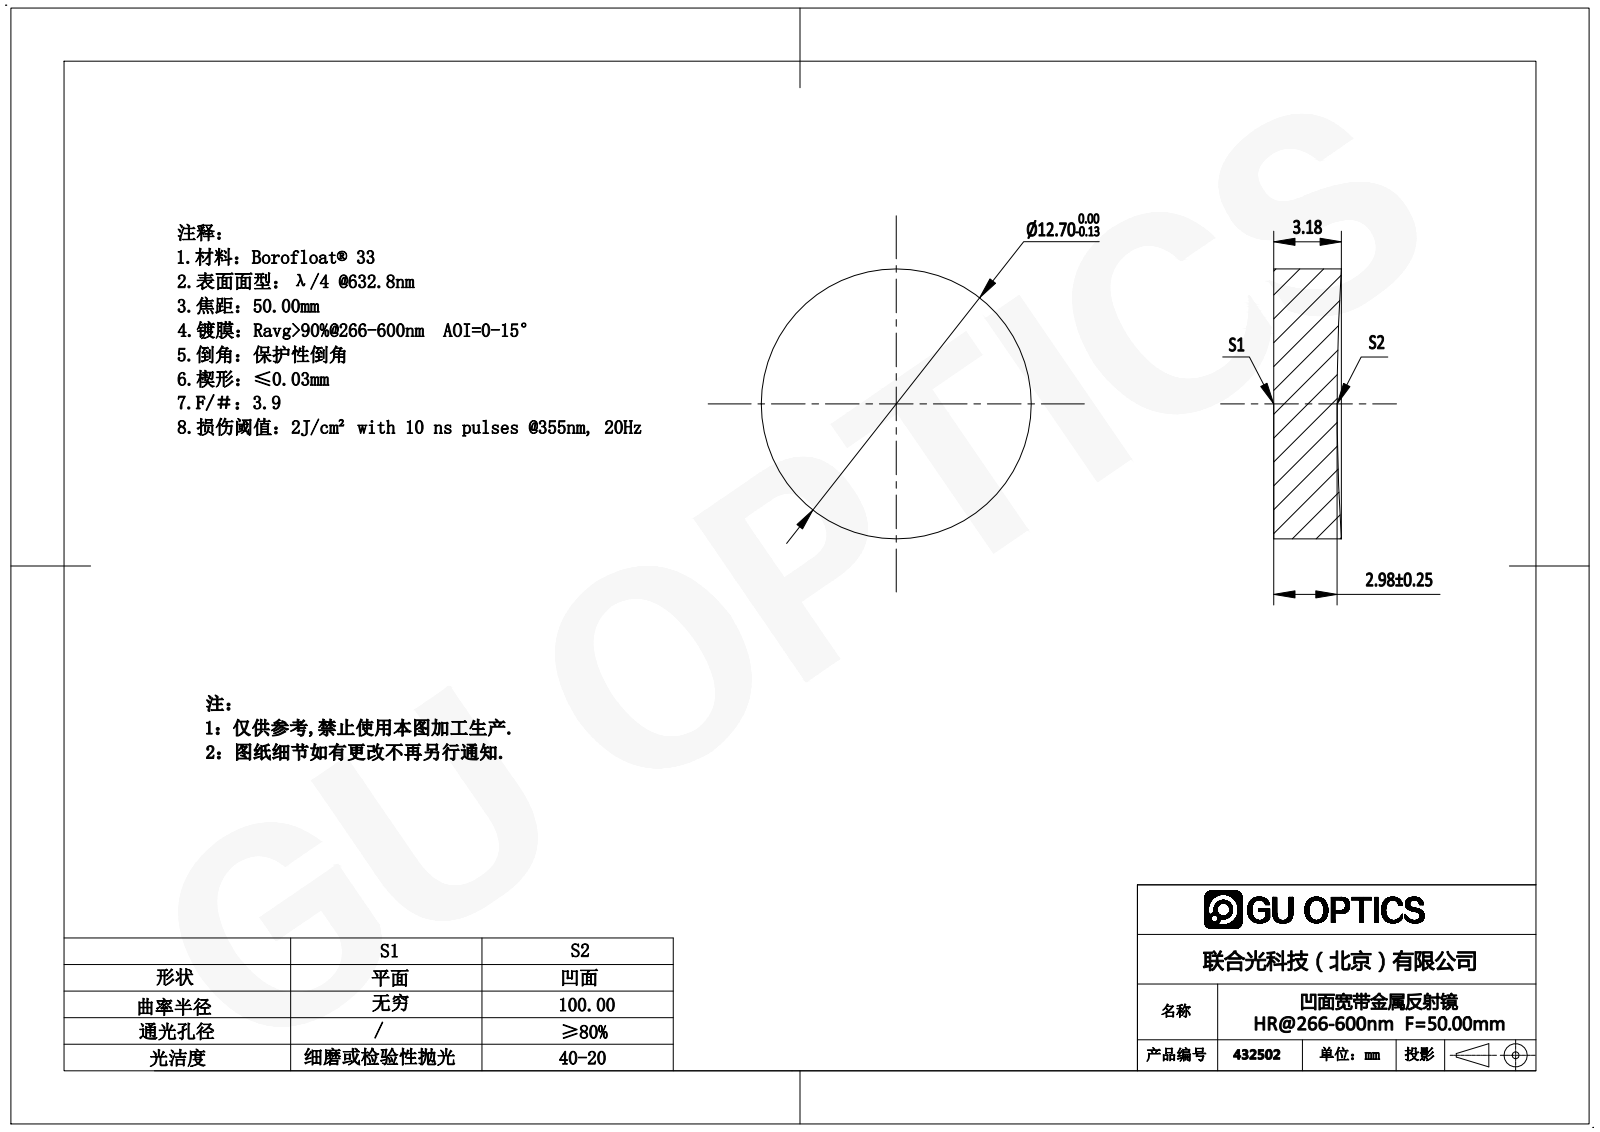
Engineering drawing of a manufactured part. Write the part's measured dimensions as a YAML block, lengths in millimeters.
part_name: "432502"
step_written_by: "SolidWorks 2016 (AUTOMOTIVE_DESIGN)"
units: millimeters
bodies: {solids: 1, faces: 5, planar: 1, cylindrical: 2, other: 2}
overall_size: [12.7, 12.7, 3.18]
volume: 390
surface_area: 380
round_bosses_or_shafts:
  - {diameter: 12.7, count: 1}
